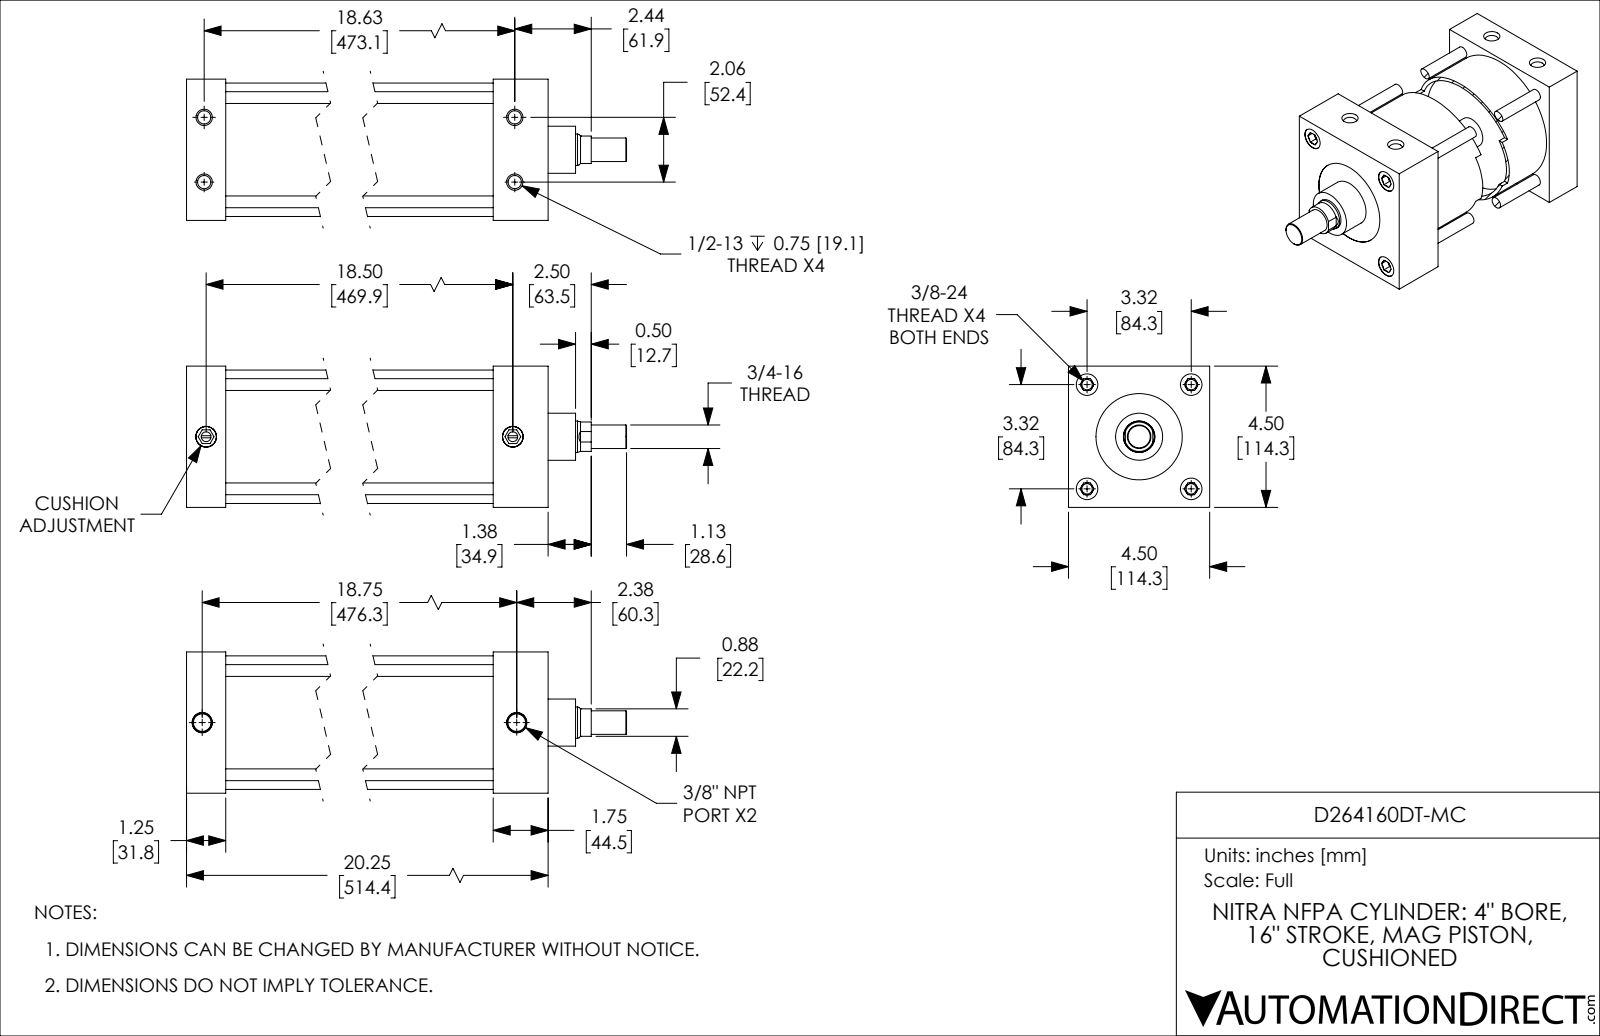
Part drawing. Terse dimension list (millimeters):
name: D264160DT-MC_CUSHION; D264160DT-MC_PISTON_KK1; D264160DT-MC; D264160DT-MC_BODY
written by: SolidWorks 2019 (CONFIG_CONTROL_DESIGN)
unit: mm
bodies: 4 solids, 246 faces (90 planar, 78 cylindrical, 78 other)
size: 577.9 × 114.3 × 114.3
volume: 2 040 000 mm³; area: 514 300 mm²
holes: 4× ⌀8.4, 4× ⌀10.7, 4× ⌀17.4, 2× ⌀7.9, 2× ⌀14.3, 2× ⌀16.7, 1× ⌀25.4, 1× ⌀69.9, 1× ⌀101.6
bosses: 4× ⌀9.5, 2× ⌀16.7, 1× ⌀108, 1× ⌀101.6, 1× ⌀38.1, 1× ⌀25.4, 1× ⌀19.1
rounds: 1× R11.9
face distances: 31.8, 114.3, 469.9, 438.2, 514.4, 482.6, 44.5, 63.5, 406.4, 450.9
hole spacings: 26.2, 59.6, 84.3, 475.4, 52.4, 119.3, 473.1, 476
